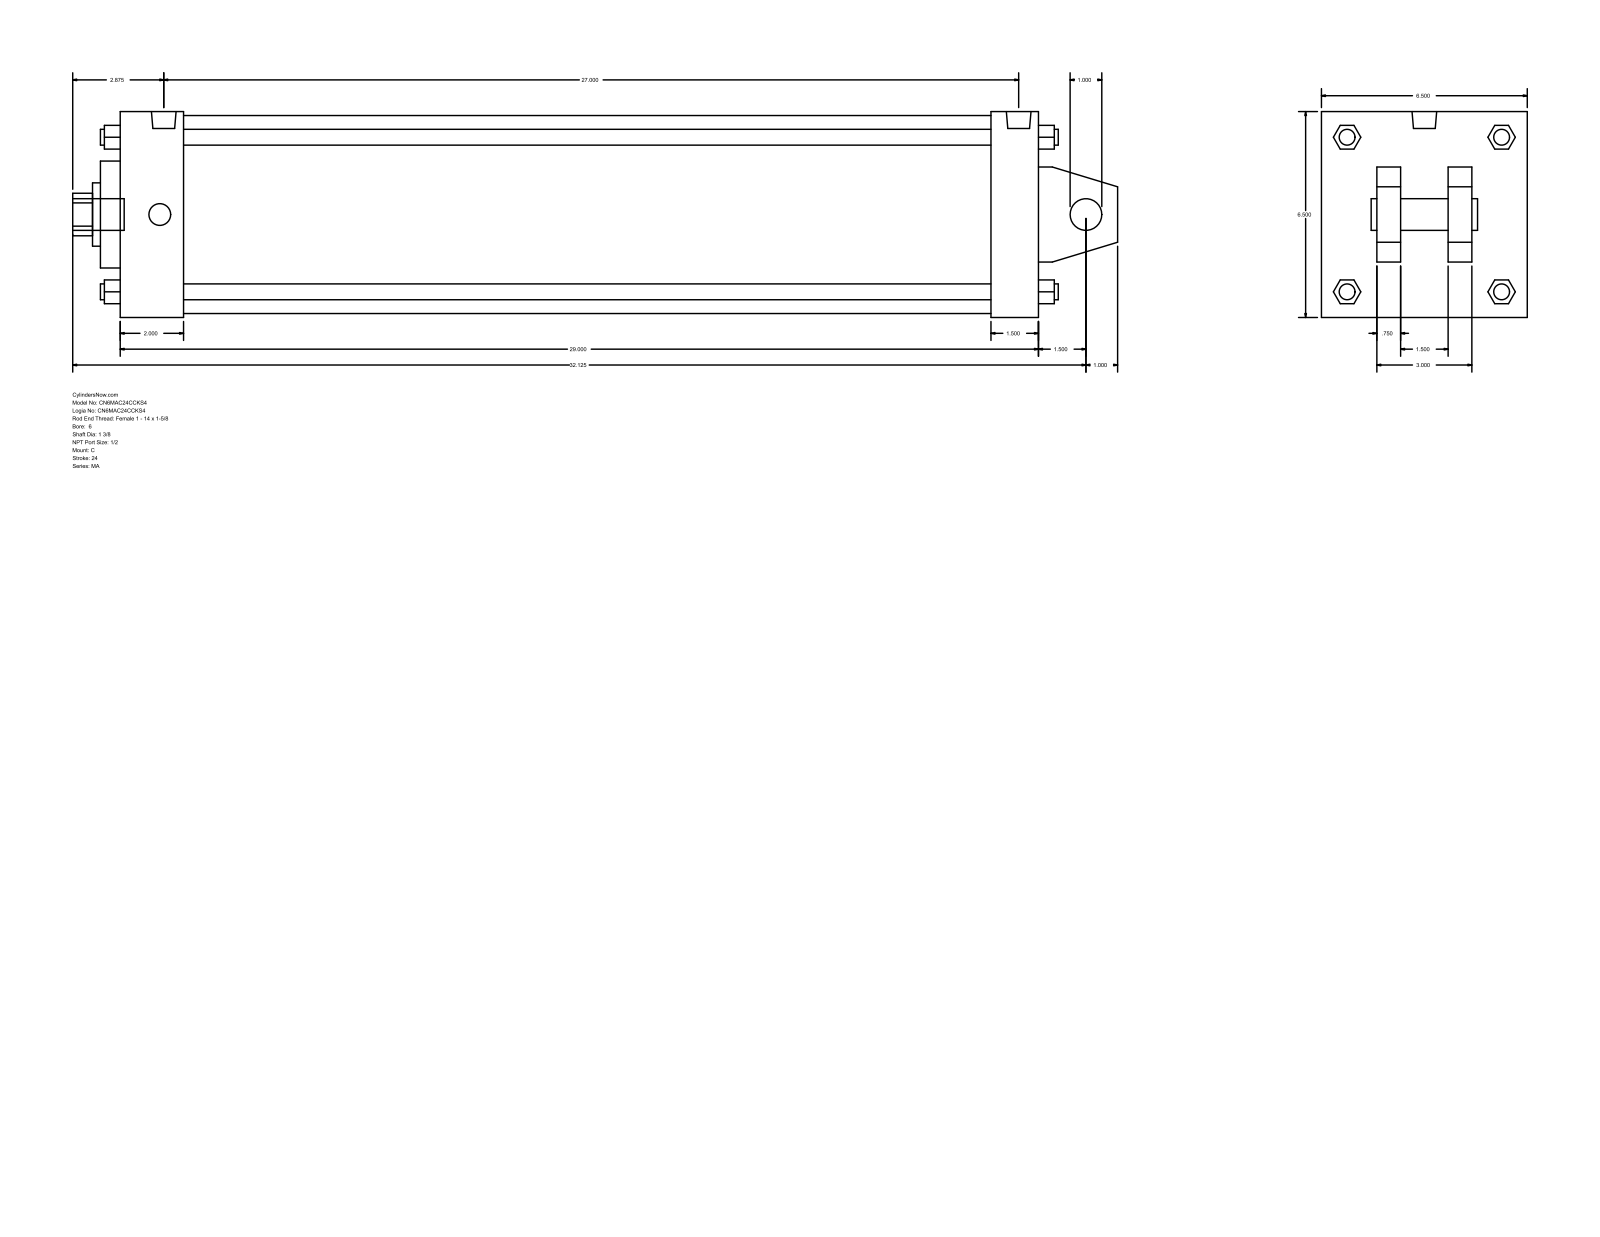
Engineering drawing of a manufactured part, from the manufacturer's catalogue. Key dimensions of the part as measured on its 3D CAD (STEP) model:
Part name (STEP PRODUCT): MA_C__0600_1.375
STEP written by: GSSL Pune (CONFIG_CONTROL_DESIGN)
Units: millimetres
Bodies: 0 solids, 141 faces (109 planar, 32 cylindrical, 0 other)
Overall size (bounding box): 838.2 × 165.1 × 165.1
Round holes (diameter × count): ⌀25.4 ×1, ⌀34.92 ×1, ⌀50.8 ×1, ⌀85.72 ×1, ⌀158.75 ×1
Round bosses / shafts (diameter × count): ⌀17.46 ×4, ⌀12.7 ×4, ⌀19.77 ×2, ⌀25.4 ×1
Partial cylindrical surfaces — rounded edges, fillets, slot ends (radius × count): R17.06 ×1
Main face-to-face distances: 165.1, 736.6, 38.1, 19.05, 63.5, 101.6, 50.8, 44.45, 120.65, 698.5
